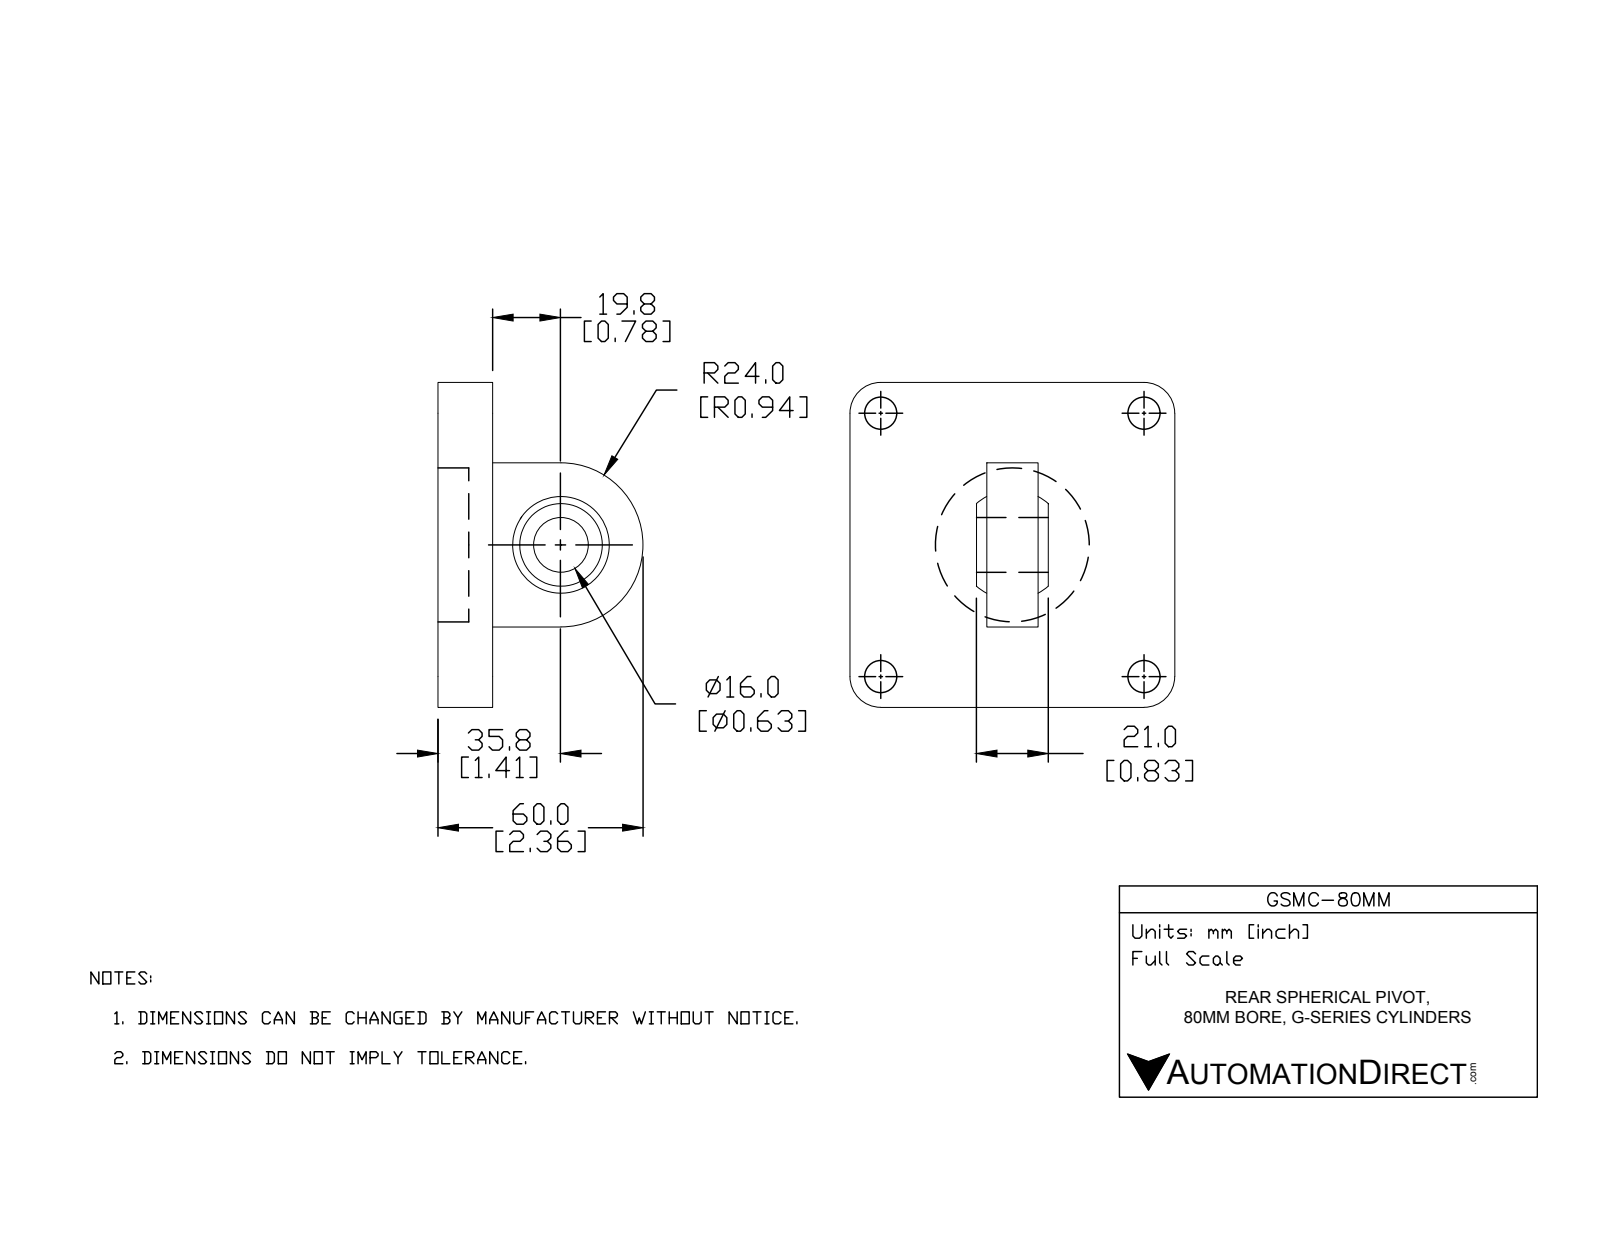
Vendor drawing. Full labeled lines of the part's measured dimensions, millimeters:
Part name (STEP PRODUCT): GSMC-80MM
STEP written by: SolidWorks 2017 (AUTOMOTIVE_DESIGN)
Units: millimetres
Bodies: 2 solids, 36 faces (13 planar, 21 cylindrical, 2 other)
Overall size (bounding box): 95 × 95 × 60
Volume: 150 889 mm³ · Surface area: 34 529 mm²
Round holes (diameter × count): ⌀9 ×4, ⌀16 ×1, ⌀28.5 ×1, ⌀45 ×1
Round bosses / shafts (diameter × count): ⌀28 ×1
Partial cylindrical surfaces — rounded edges, fillets, slot ends (radius × count): R12 ×4, R24 ×1
Main face-to-face distances: 16, 95, 40, 55, 9, 7, 15, 37, 58, 3
Hole centre spacings: 54.45, 77, 108.89
